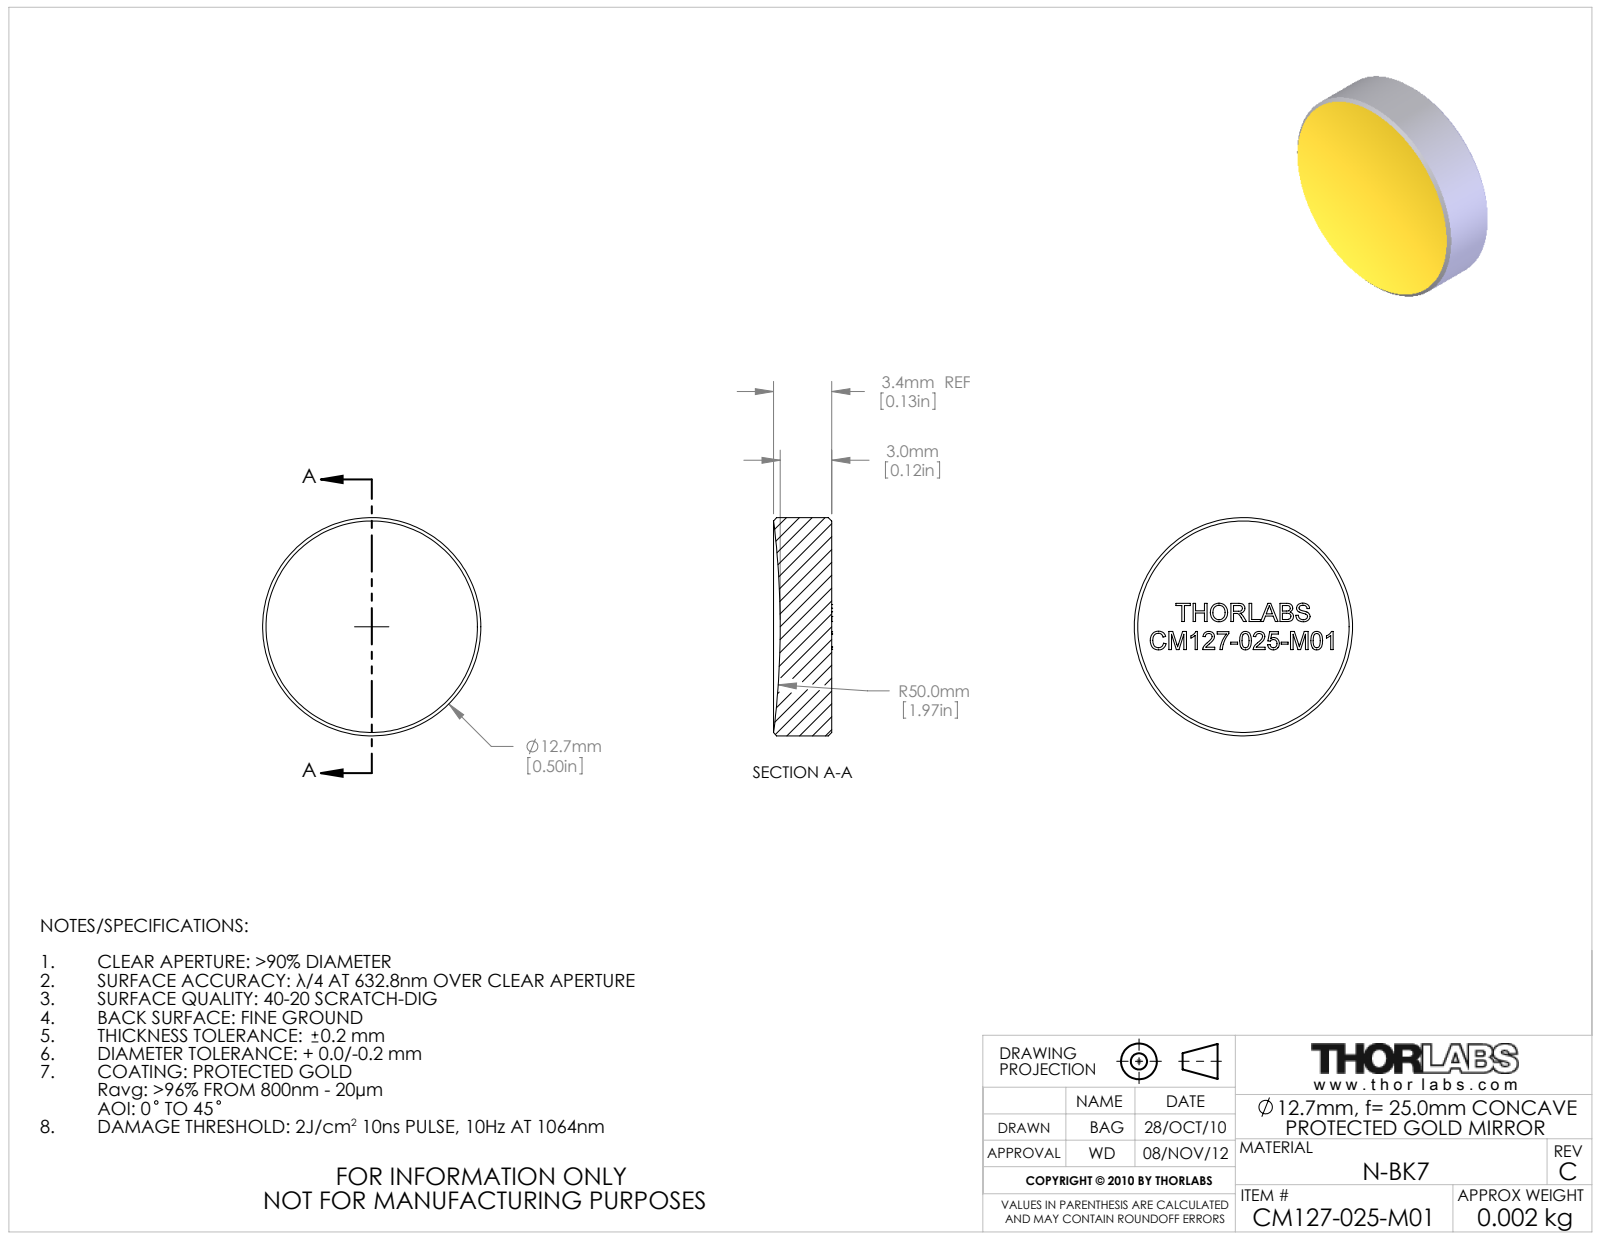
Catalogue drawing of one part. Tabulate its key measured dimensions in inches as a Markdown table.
| quantity | value |
| --- | --- |
| part name | 17580-E0W |
| STEP written by | SolidWorks 2009 (AUTOMOTIVE_DESIGN) |
| units | inches |
| bodies | 1 solid, 270 faces (154 planar, 2 cylindrical, 114 other) |
| overall size | 0.5 × 0.5 × 0.133 |
| volume | 0.025 in³ |
| surface area | 0.588 in² |
| round bosses / shafts (diameter × count) | 0.5 × 1 |
| main face-to-face distances | 0.042, 0.064, 0.052, 0.048, 0.036, 0.102, 0.03, 0.279, 0.028, 0.034 |
